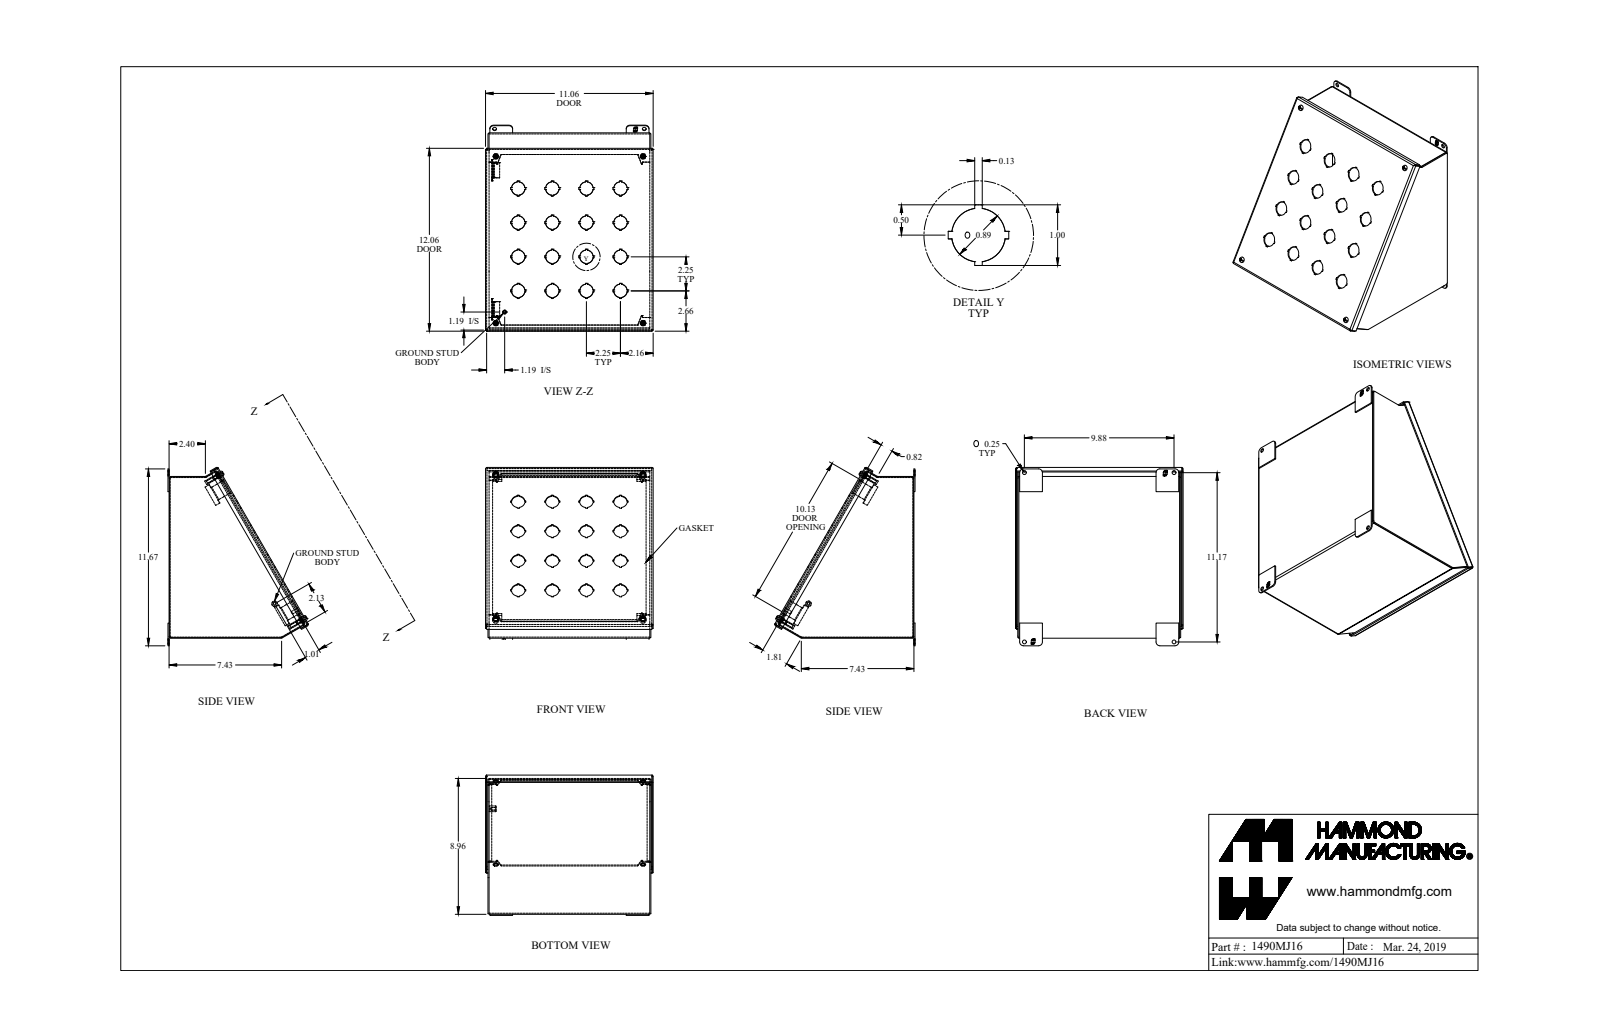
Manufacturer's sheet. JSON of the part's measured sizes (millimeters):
{"part_name": "1490MJ16_Default", "step_written_by": "SolidWorks 2019 (CONFIG_CONTROL_DESIGN)", "units": "millimeters", "bodies": {"solids": 26, "faces": 949, "planar": 675, "cylindrical": 236, "other": 38}, "overall_size": [299.4, 281, 236.3], "volume_mm3": 643200, "surface_area_mm2": 720000, "round_holes": [[22.2, 9], [6.4, 8], [22.2, 7], [4, 4], [3, 1], [3.5, 1], [4, 1]], "round_bosses_or_shafts": [[9.9, 4], [7, 4], [4.8, 4], [3.8, 4], [9.5, 1], [7.4, 1]], "partial_cylinders_radius": [[2.7, 18], [0.9, 12], [0.7, 9], [2.2, 9], [6.4, 8], [3.2, 4], [4.1, 4], [4.3, 4]], "face_to_face_distances": [1.8, 271.2, 269.4, 273.1, 269.1, 270.9, 267.3, 296.6, 5.6, 275], "hole_center_spacings": [127.8, 57.2, 80.8, 114.3, 180.7, 171.5, 188.2, 206.1]}
